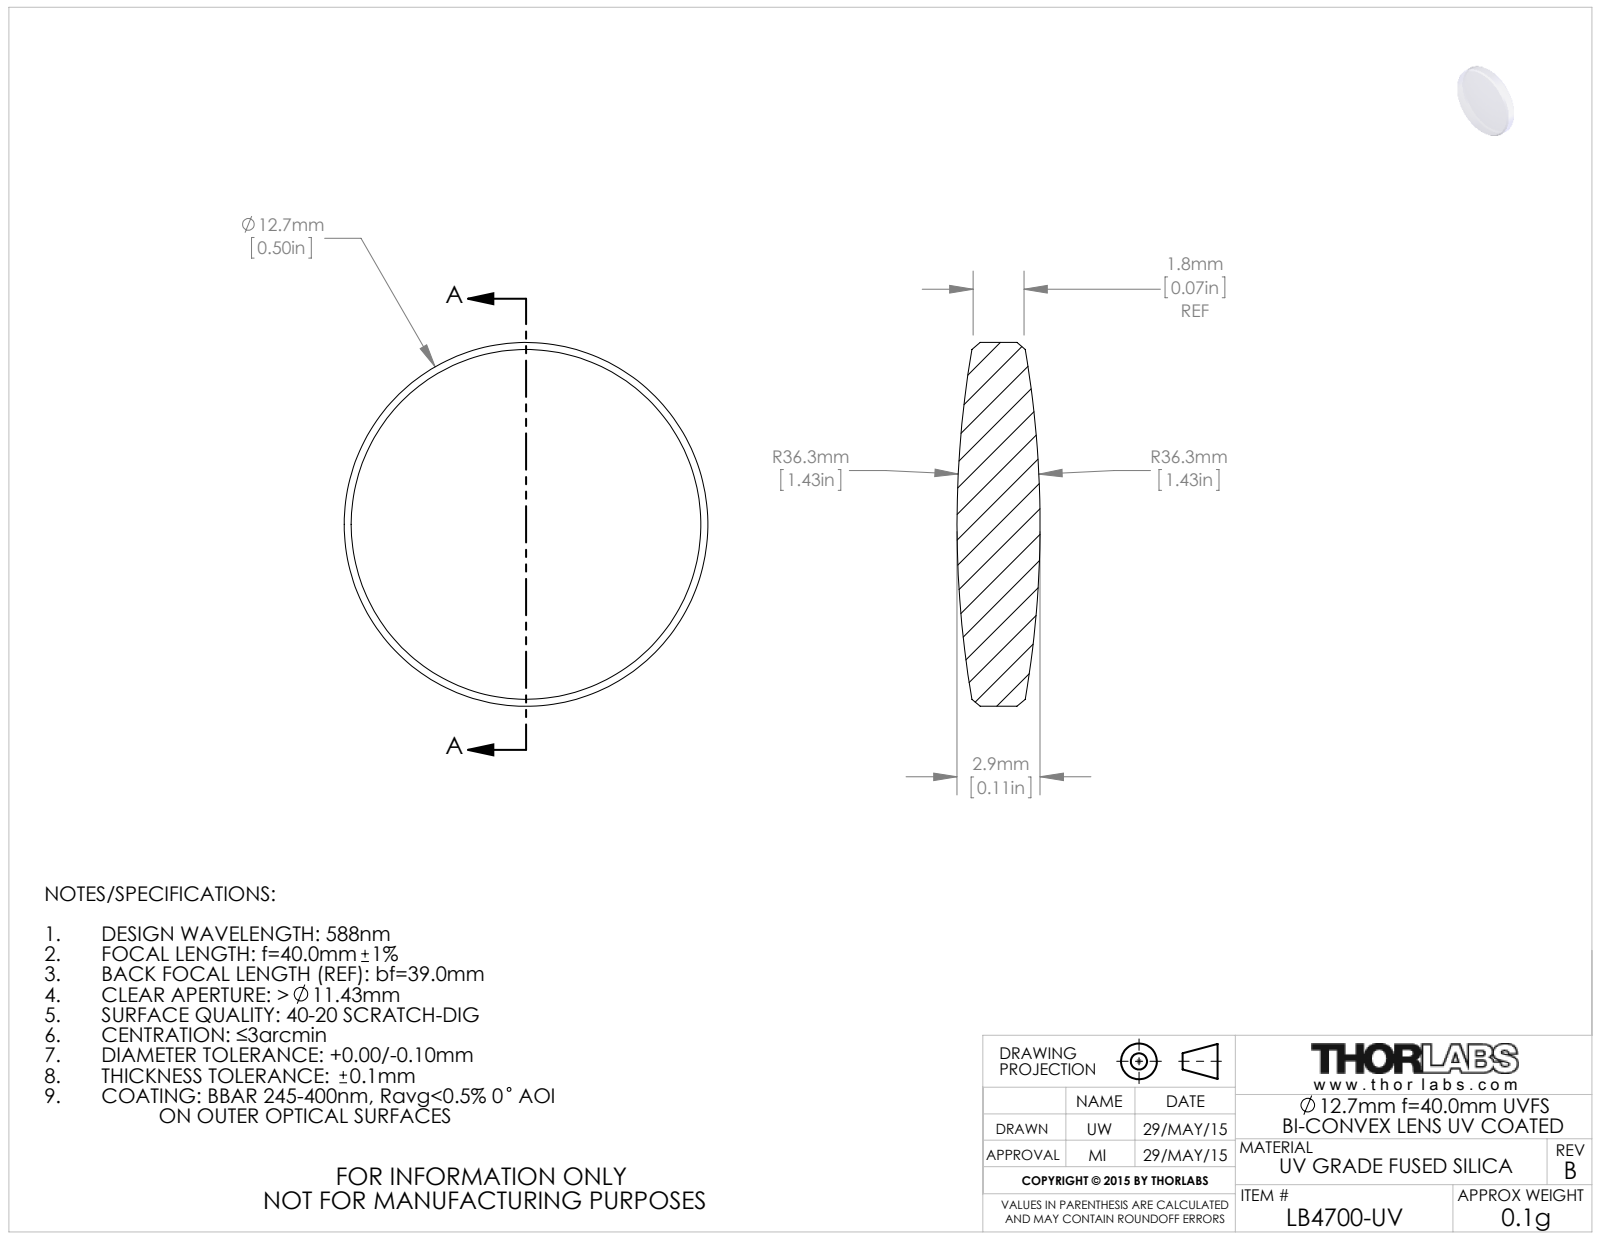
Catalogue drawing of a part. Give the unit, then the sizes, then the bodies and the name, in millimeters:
Units: millimetres
Overall size (bounding box): 12.7 × 12.7 × 2.9
Round bosses / shafts (diameter × count): ⌀12.7 ×1
Volume: 294 mm³ · Surface area: 317 mm²
Bodies: 1 solid, 10 faces (0 planar, 2 cylindrical, 8 other)
Part name (STEP PRODUCT): 4313-E0W
STEP written by: SolidWorks 2014 (CONFIG_CONTROL_DESIGN)
